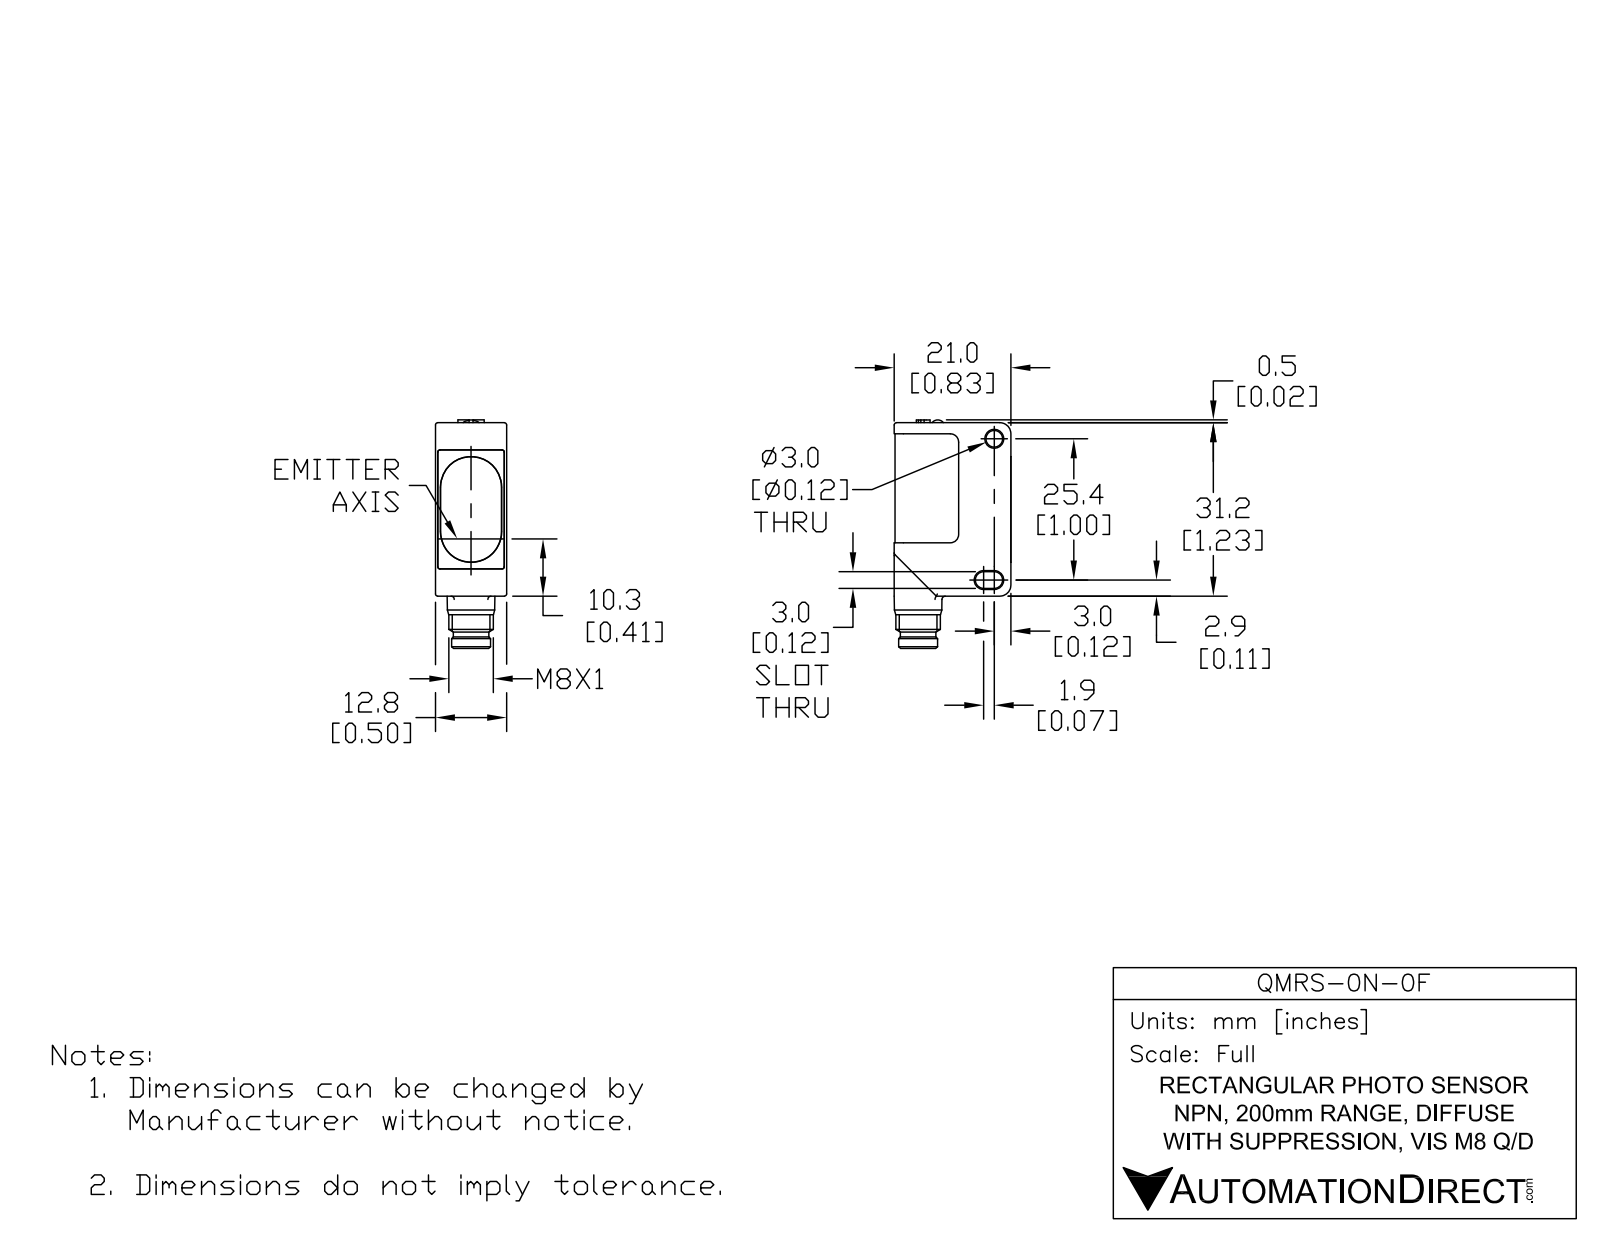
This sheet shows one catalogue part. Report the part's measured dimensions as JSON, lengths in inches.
{"part_name": "QMRS-0N-0F", "step_written_by": "SolidWorks 2017 (AUTOMOTIVE_DESIGN)", "units": "inches", "bodies": {"solids": 7, "faces": 262, "planar": 123, "cylindrical": 92, "other": 47}, "overall_size": [1.618, 0.827, 0.504], "volume_in3": 0.468, "surface_area_in2": 7.721, "round_holes": [[0.118, 1], [0.173, 1], [0.228, 1]], "round_bosses_or_shafts": [[0.039, 4], [0.315, 1], [0.276, 1], [0.252, 1], [0.122, 1], [0.11, 1]], "partial_cylinders_radius": [[0.016, 10], [0.059, 7], [0.024, 4], [0.039, 4], [0.177, 4], [0.02, 3], [0.065, 2], [0.079, 2]], "face_to_face_distances": [0.498, 0.504, 0.02, 0.11, 0.039, 0.016, 0.071, 0.492, 0.488, 0.482], "hole_center_spacings": [0.311]}
